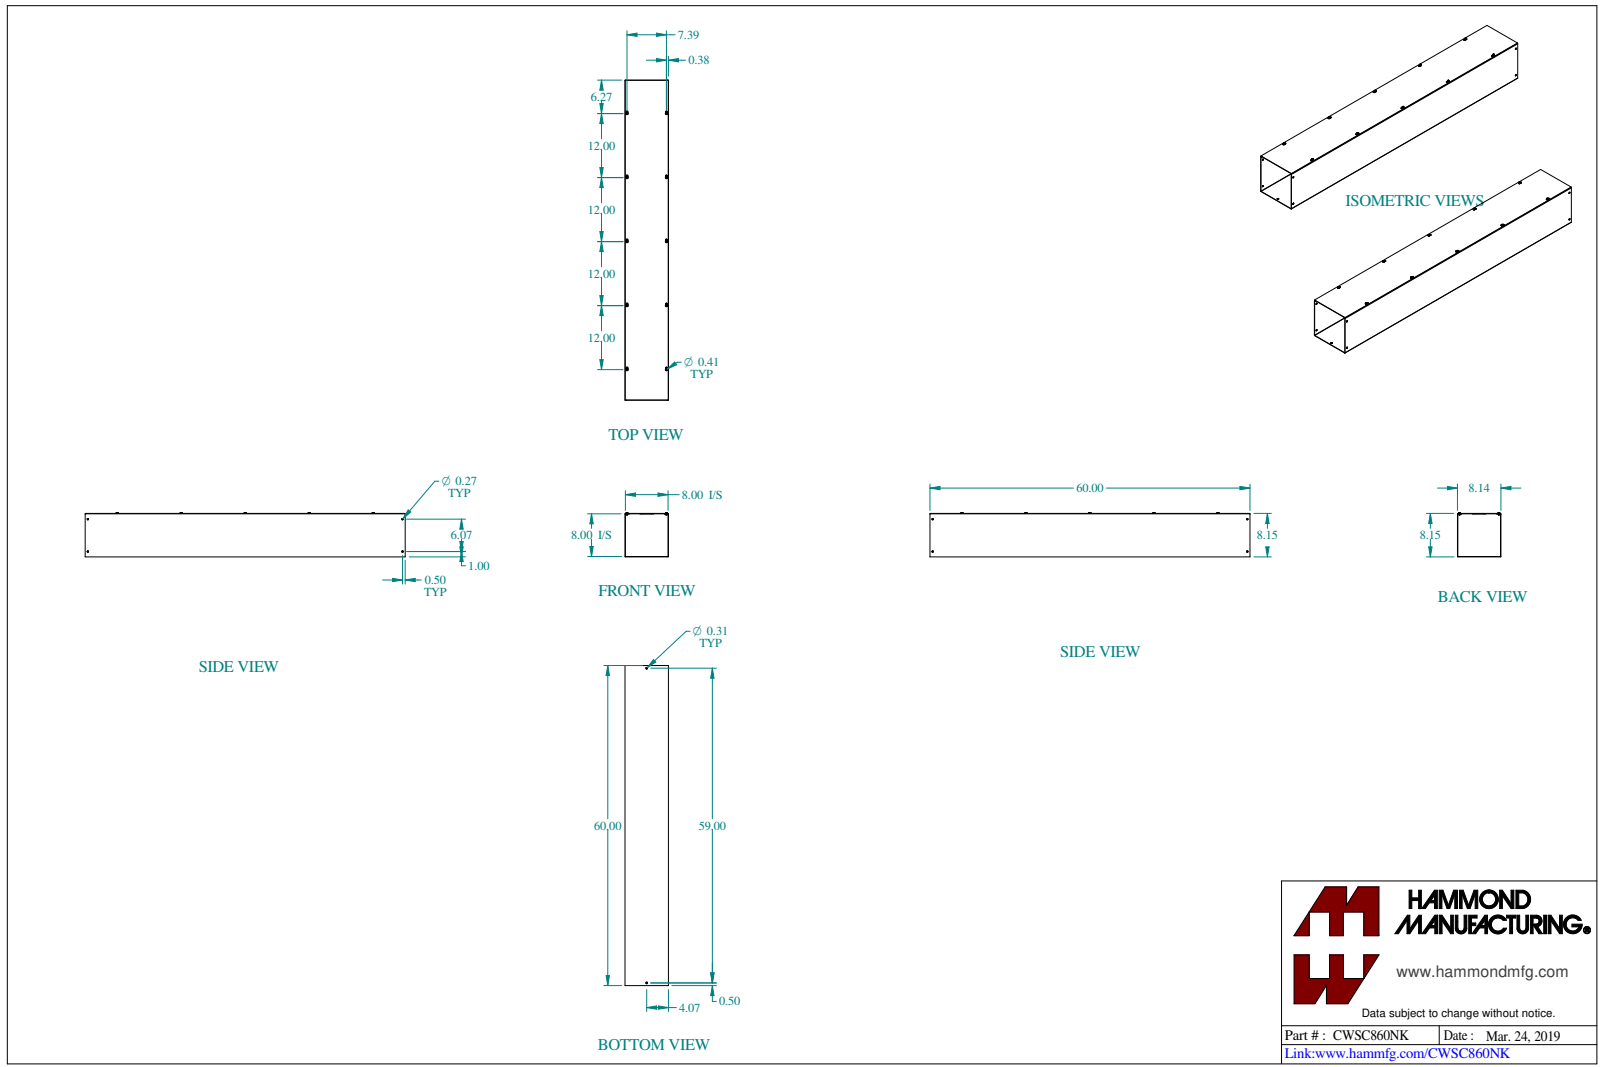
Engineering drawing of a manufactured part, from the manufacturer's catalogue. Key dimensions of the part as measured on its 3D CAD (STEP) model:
Part name (STEP PRODUCT): CWSC860NK
STEP written by: SolidWorks 2023 (CONFIG_CONTROL_DESIGN)
Units: inches
Bodies: 12 solids, 366 faces (178 planar, 128 cylindrical, 60 other)
Overall size (bounding box): 60 × 8.325 × 8.144
Volume: 147.3 in³ · Surface area: 4 036 in²
Round holes (diameter × count): ⌀0.177 ×10, ⌀0.266 ×4, ⌀0.313 ×2
Round bosses / shafts (diameter × count): ⌀0.375 ×10, ⌀0.19 ×10
Partial cylindrical surfaces — rounded edges, fillets, slot ends (radius × count): R0.125 ×10, R0.203 ×10, R0.036 ×4, R0.108 ×4
Main face-to-face distances: 0.072, 8.072, 8, 0.078, 8.15, 8.078, 8.144, 7.928, 0.15, 0.031
Hole centre spacings: 12, 14.095, 24, 25.113, 7.394, 6.627, 17.886, 29.731
